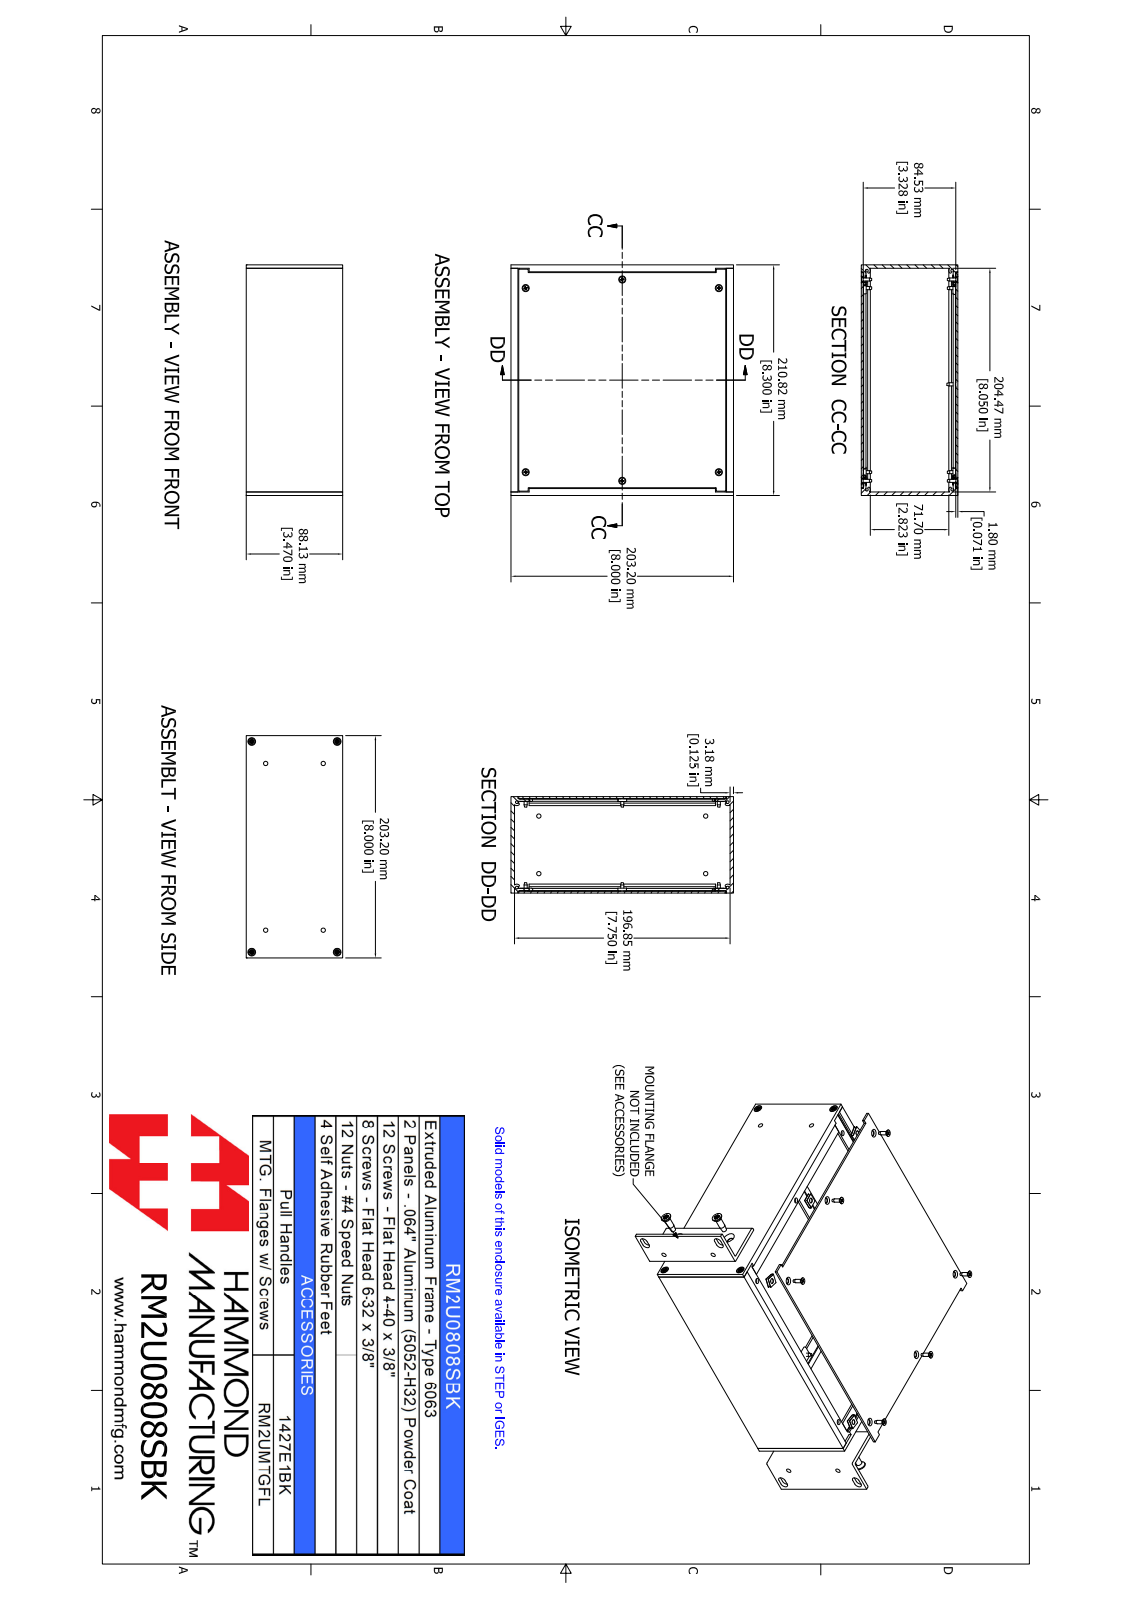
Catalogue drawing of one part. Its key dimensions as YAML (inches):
part_name: "RM2U0808SBK"
step_written_by: "SolidWorks 2021 (AUTOMOTIVE_DESIGN)"
units: inches
bodies: {solids: 39, faces: 1003, planar: 478, cylindrical: 158, other: 367}
overall_size: [8.3, 8, 3.47]
volume: 26.19
surface_area: 560.6
round_holes:
  - {diameter: 0.098, count: 6}
  - {diameter: 0.157, count: 6}
  - {diameter: 0.169, count: 6}
  - {diameter: 0.138, count: 4}
  - {diameter: 0.156, count: 4}
round_bosses_or_shafts:
  - {diameter: 0.214, count: 7}
  - {diameter: 0.112, count: 7}
  - {diameter: 0.238, count: 4}
  - {diameter: 0.138, count: 4}
partial_cylinders:
  - {radius: 0.039, count: 12}
  - {radius: 0.049, count: 12}
  - {radius: 0.05, count: 8}
  - {radius: 0.125, count: 8}
  - {radius: 0.037, count: 6}
  - {radius: 0.038, count: 4}
face_to_face_distances: [0.071, 3.399, 0.125, 3.47, 3.328, 7.875, 8, 0.125, 8.3, 8.05]
hole_center_spacings: [3.486, 6.809, 7.261, 0.935, 0.936, 2.071, 2.69, 2.691]
